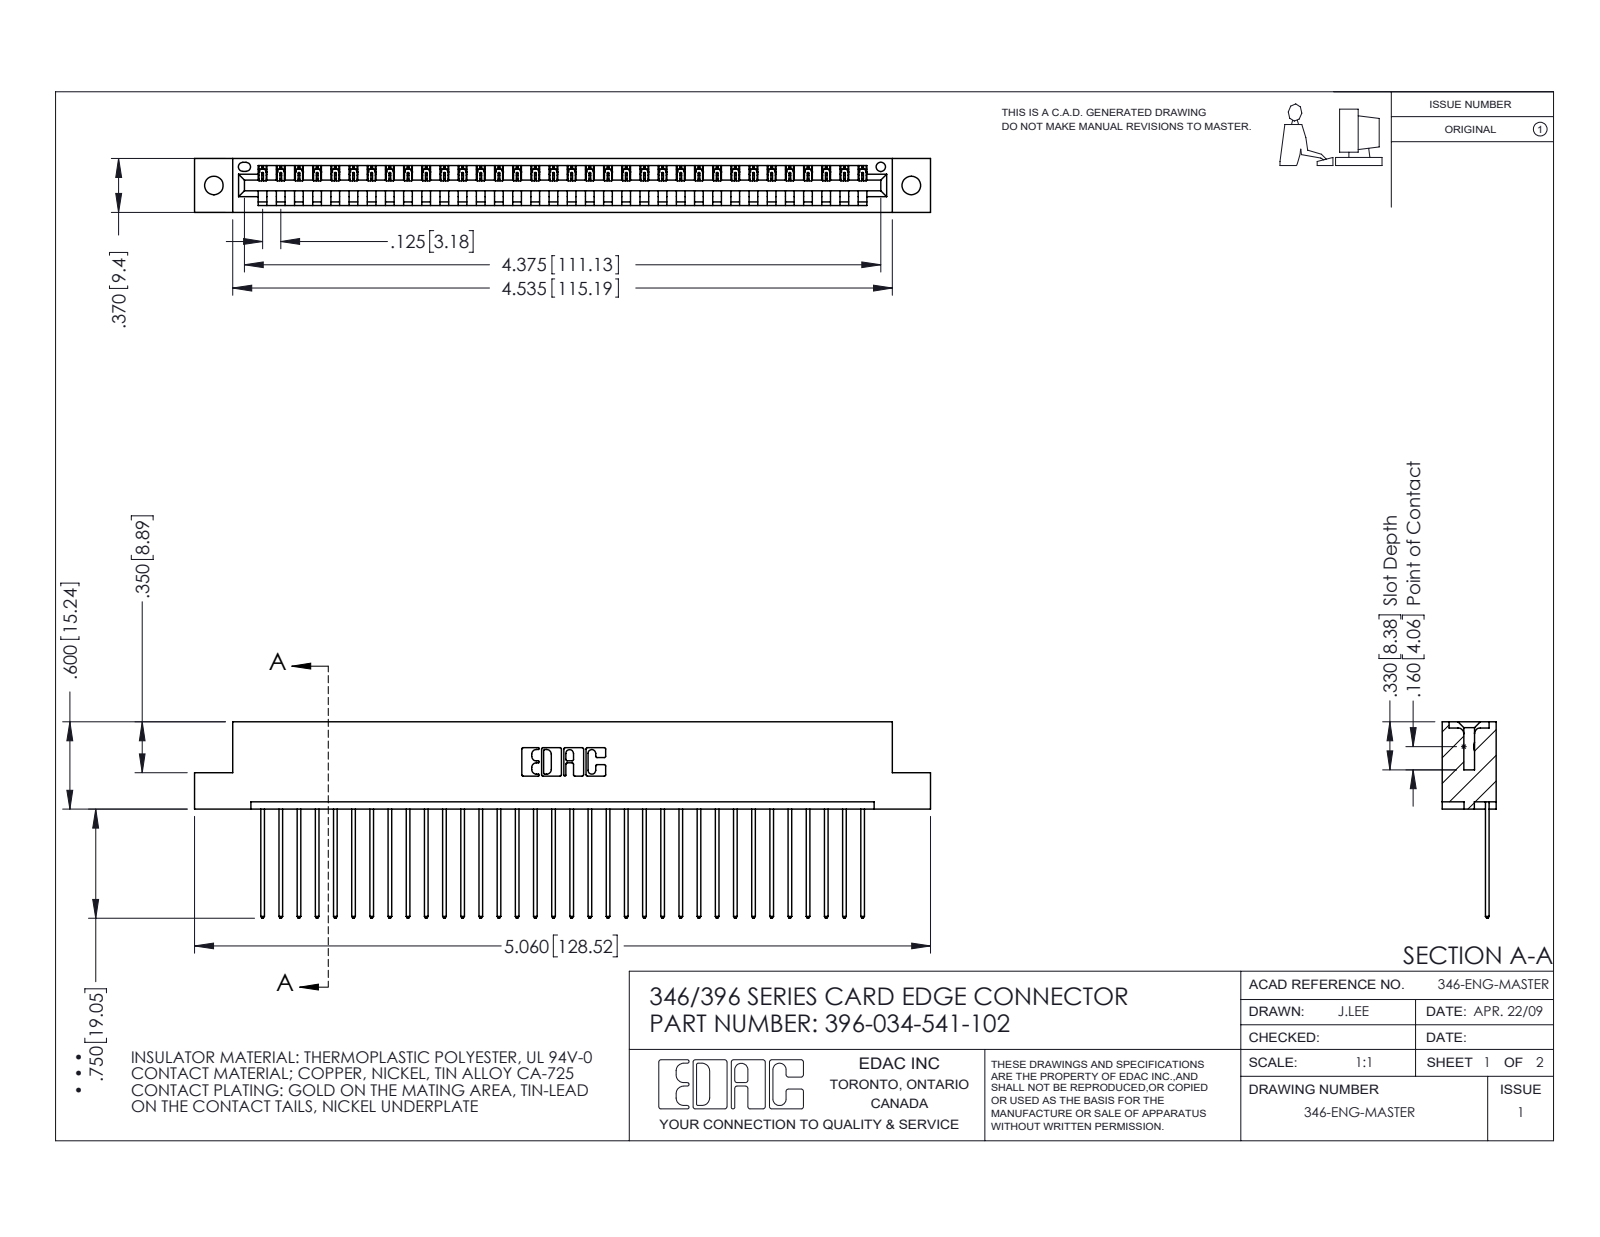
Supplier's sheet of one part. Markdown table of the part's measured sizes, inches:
| quantity | value |
| --- | --- |
| part name | 396-034-541-102; 345-292-001_345-293-141; 346 Part_Flush Mounting Lugs - 0.128 Dia |
| STEP written by | SolidWorks 2016 (CONFIG_CONTROL_DESIGN) |
| units | inches |
| bodies | 35 solids, 2094 faces (1436 planar, 658 cylindrical, 0 other) |
| overall size | 5.06 × 1.35 × 0.37 |
| volume | 0.752 in³ |
| surface area | 24.36 in² |
| round holes (diameter × count) | 0.128 × 2, 0.064 × 1 |
| partial cylindrical surfaces (radius × count) | 0.006 × 68, 0.01 × 68, 0.01 × 22, 0.007 × 6, 0.031 × 6, 0.026 × 3, 0.031 × 2, 0.04 × 2 |
| main face-to-face distances | 0.048, 0.322, 0.37, 0.25, 0.072, 0.298, 0.025, 0.148, 0.222, 0.1 |
| hole center spacings | 0.246, 4.587, 4.795 |
